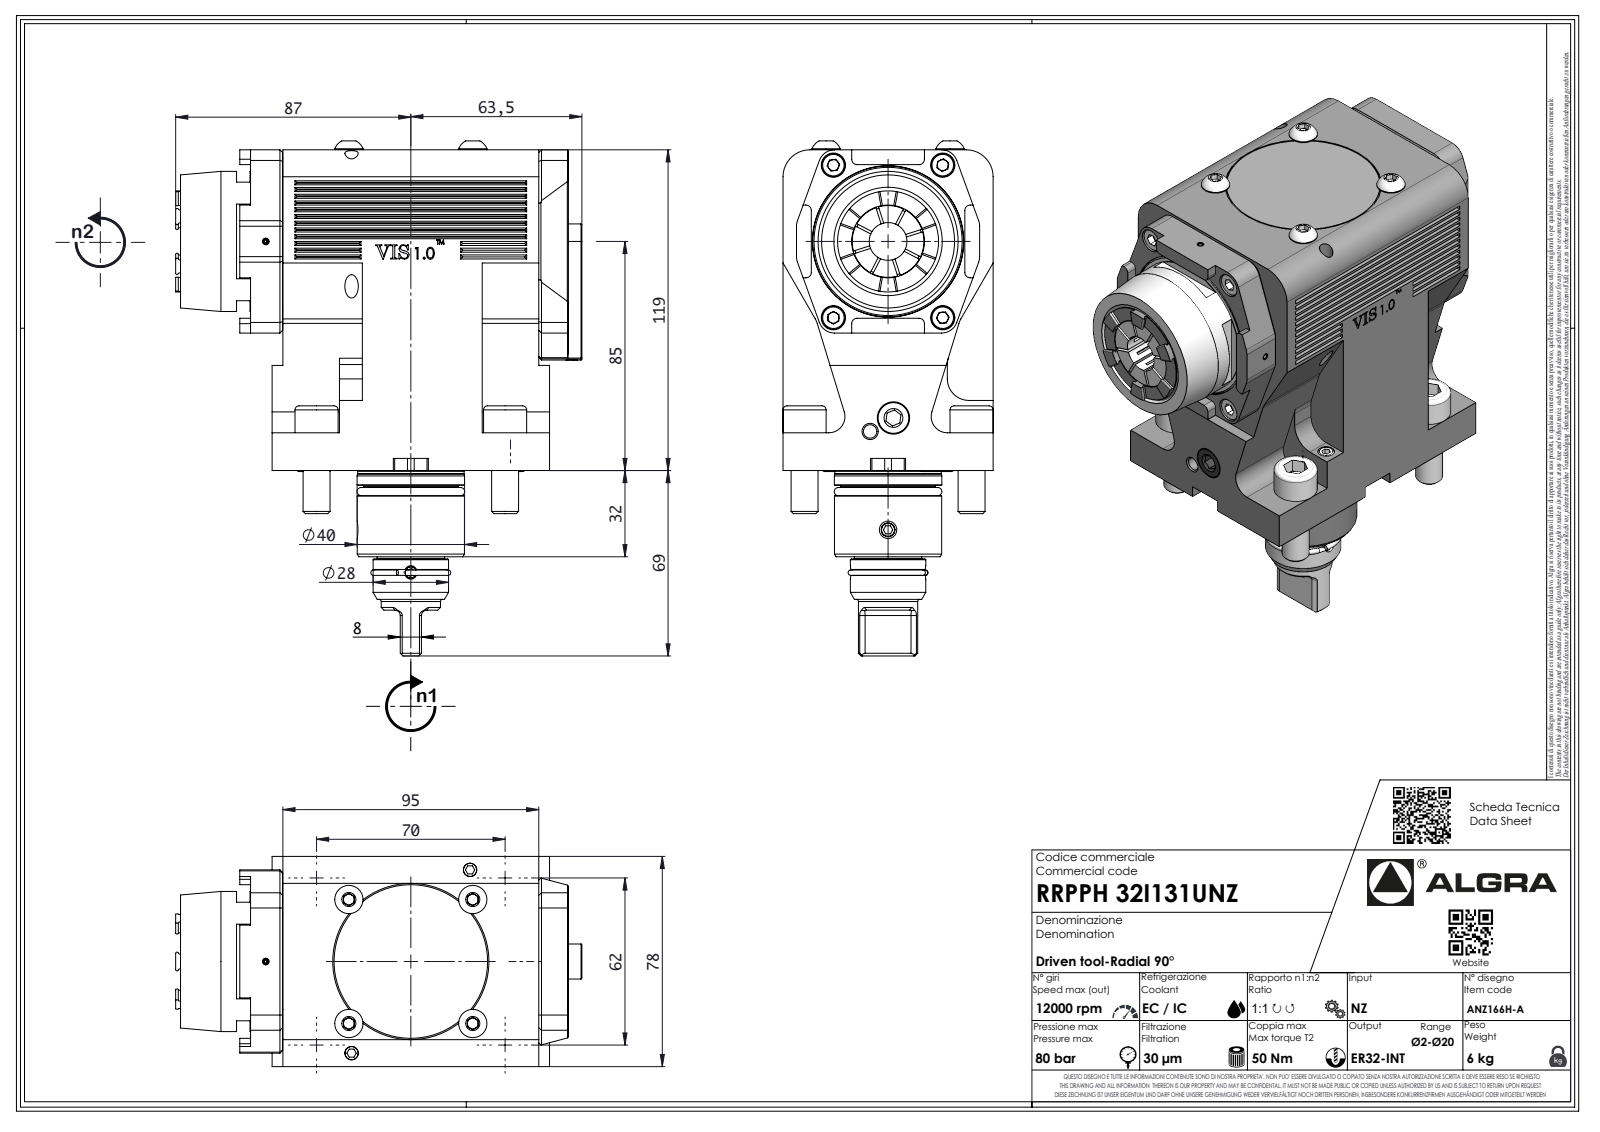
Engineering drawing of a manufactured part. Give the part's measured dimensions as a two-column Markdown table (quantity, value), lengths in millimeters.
| quantity | value |
| --- | --- |
| part name | RRPPH32I131UNZ |
| STEP written by | SolidWorks 2023 (AUTOMOTIVE_DESIGN) |
| units | millimeters |
| bodies | 1 solid, 631 faces (379 planar, 111 cylindrical, 141 other) |
| overall size | 187.8 × 150.81 × 78 |
| volume | 1 005 000 mm³ |
| surface area | 85 857 mm² |
| round holes (diameter × count) | 2.1 × 1, 6 × 1 |
| round bosses / shafts (diameter × count) | 52 × 1, 39.9 × 1, 39.8 × 1, 39.5 × 1, 35.1 × 1, 35 × 1, 28 × 1, 25 × 1 |
| partial cylindrical surfaces (radius × count) | 5 × 16, 2 × 14, 6 × 10, 0.33 × 7, 0.52 × 7, 3.7 × 7, 8 × 6, 10 × 4 |
| main face-to-face distances | 78, 119, 4, 12, 99, 106, 25, 106.1, 111, 21 |
